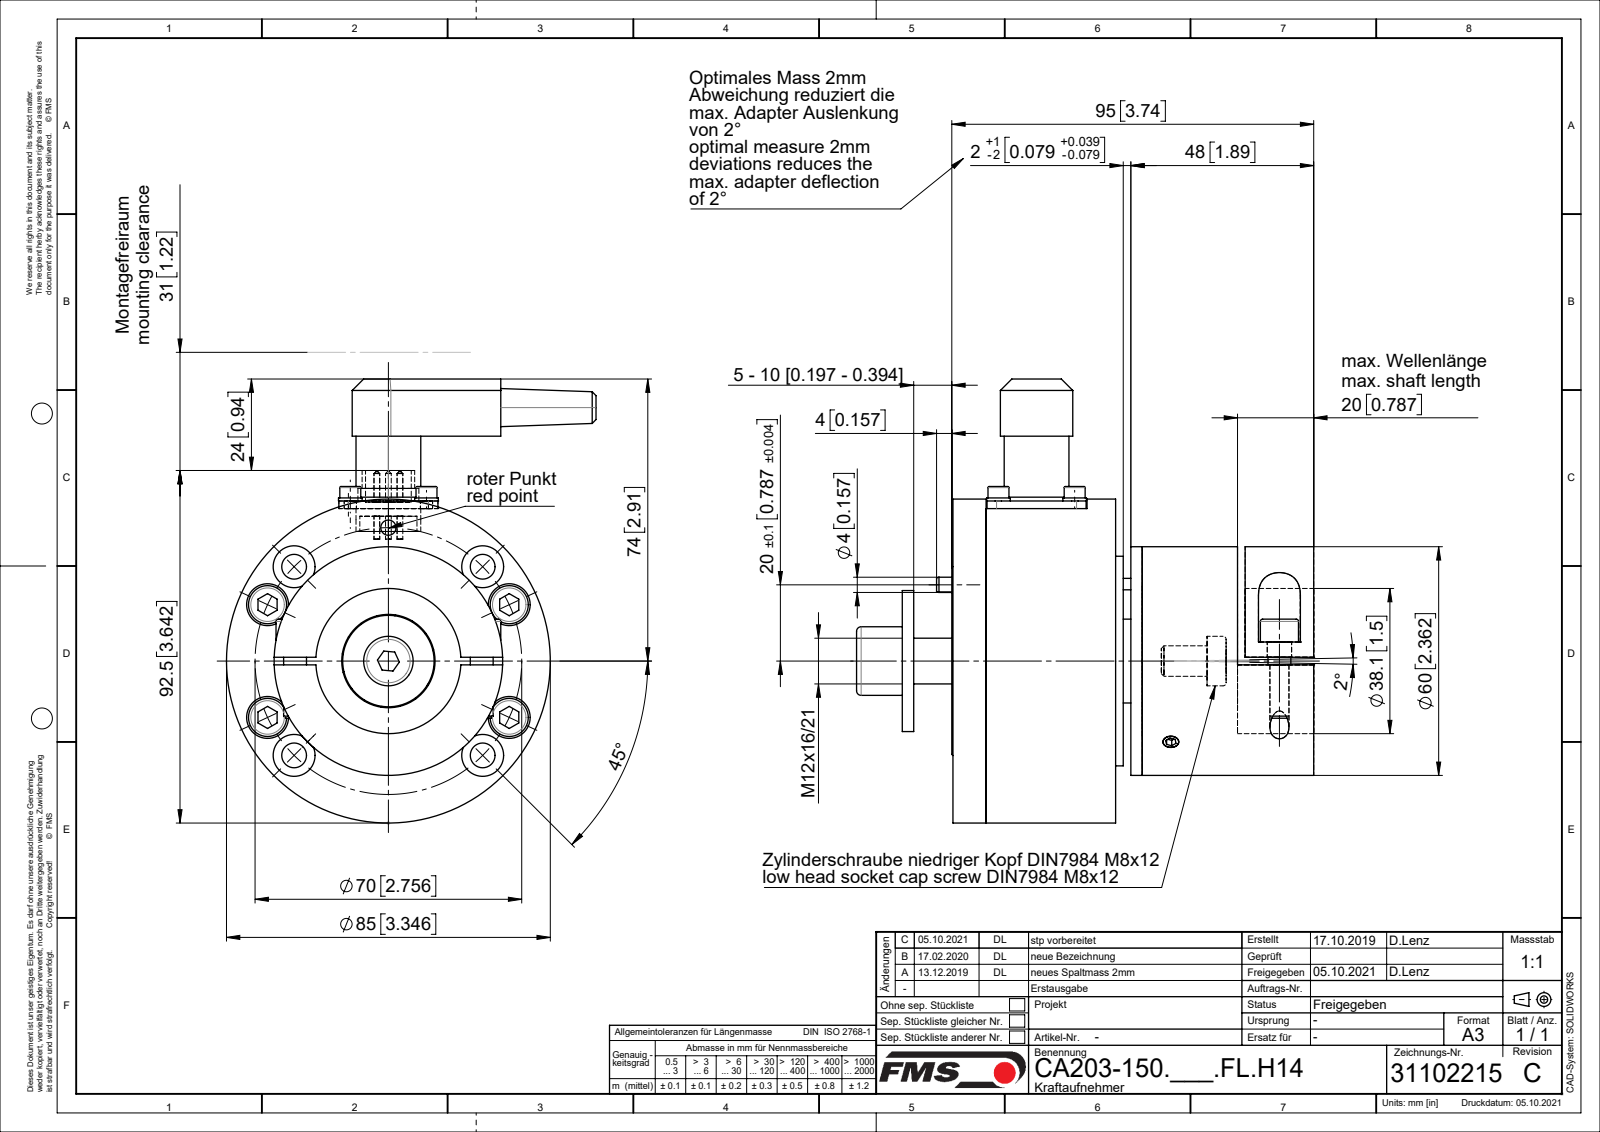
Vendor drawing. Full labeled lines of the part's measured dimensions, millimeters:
Part name (STEP PRODUCT): Zyl-Schr DIN912_M3x6; 070908-1_stp_01; Federringe_DIN127A_M03; Zyl-Schr DIN912_M6x20 (+8 more)
STEP written by: SolidWorks 2018 (CONFIG_CONTROL_DESIGN)
Units: millimetres
Bodies: 43 solids, 803 faces (278 planar, 333 cylindrical, 192 other)
Overall size (bounding box): 120 × 116.5 × 97
Volume: 303 434 mm³ · Surface area: 113 477 mm²
Round holes (diameter × count): ⌀2.5 ×8, ⌀6.5 ×8, ⌀11 ×8, ⌀5 ×6, ⌀2 ×5, ⌀4 ×5, ⌀3.1 ×4, ⌀3.2 ×4, ⌀3.6 ×4, ⌀7 ×4, ⌀3 ×2, ⌀6.4 ×2
Round bosses / shafts (diameter × count): ⌀3 ×8, ⌀6 ×7, ⌀10 ×6, ⌀1.5 ×5, ⌀6.2 ×4, ⌀5.7 ×4, ⌀5.5 ×4, ⌀85 ×1
Partial cylindrical surfaces — rounded edges, fillets, slot ends (radius × count): R2.5 ×4, R5 ×2, R5.5 ×2, R9.5 ×1
Main face-to-face distances: 2, 10, 41, 45, 30, 3, 60, 34, 22, 15
Hole centre spacings: 35, 20, 24.78, 25.2, 32.8, 51.14, 56.46, 6
